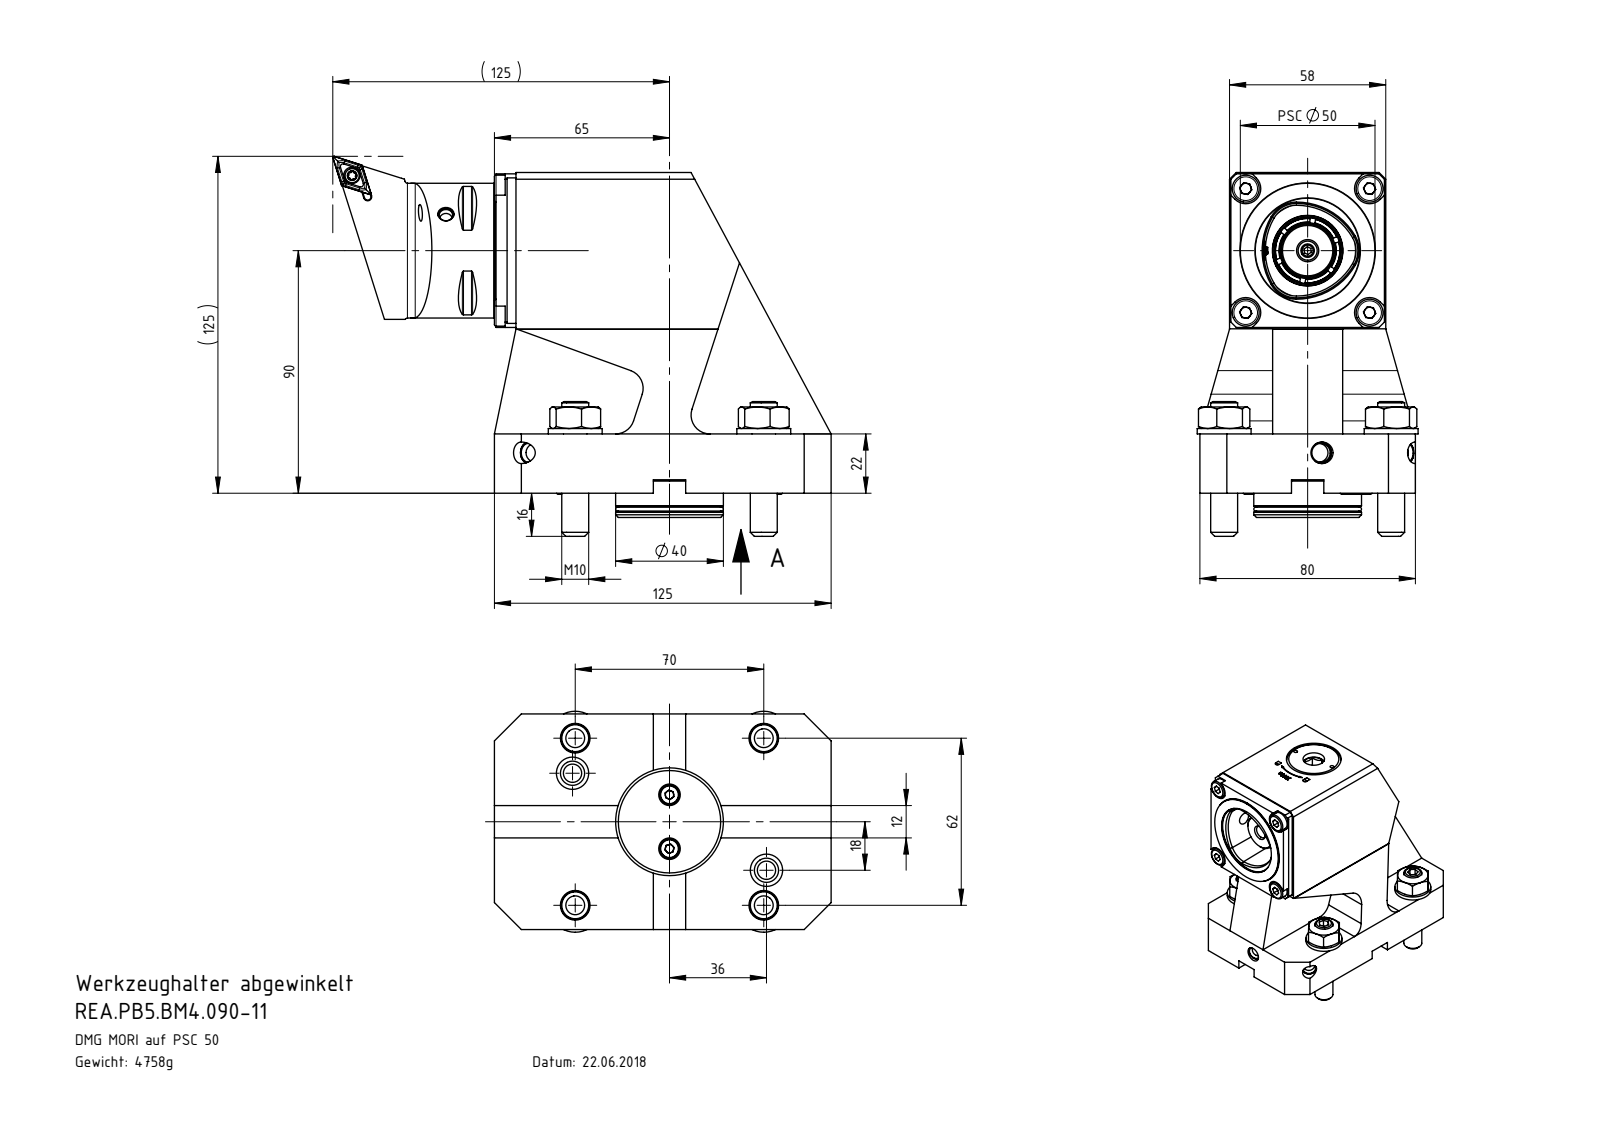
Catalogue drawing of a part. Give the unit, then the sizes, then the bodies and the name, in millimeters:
Units: millimetres
Overall size (bounding box): 135 × 125 × 82
Round holes (diameter × count): ⌀6.8 ×5, ⌀3.3 ×4, ⌀4.2 ×4, ⌀5 ×4, ⌀6.2 ×4, ⌀7 ×4, ⌀8 ×4, ⌀8.5 ×4, ⌀10.5 ×4, ⌀11 ×4, ⌀2.1 ×3, ⌀3 ×3
Round bosses / shafts (diameter × count): ⌀10 ×8, ⌀20 ×5, ⌀7 ×4, ⌀6 ×4, ⌀4 ×4, ⌀8 ×3, ⌀50 ×1, ⌀49.7 ×1
Partial cylindrical surfaces — rounded edges, fillets, slot ends (radius × count): R0.3 ×10, R5 ×4, R5.6 ×4, R0.8 ×3, R7 ×3, R0.2 ×2, R4 ×2, R4.05 ×2
Main face-to-face distances: 42, 16, 22, 27, 17, 5, 11, 53, 69, 58
Hole centre spacings: 32.53, 40.82, 46, 46.75, 53.91, 10, 12.5, 13.04
Volume: 636 221 mm³ · Surface area: 154 125 mm²
Bodies: 53 solids, 1134 faces (467 planar, 251 cylindrical, 416 other)
Part name (STEP PRODUCT): ISO 4032 - M10; U50-PS5.BER.003_A; REA.PB5.BM4.090-11; ISO 7089 - 10_PreviewCfg (+8 more)
STEP written by: SolidWorks 2017 (AUTOMOTIVE_DESIGN)
